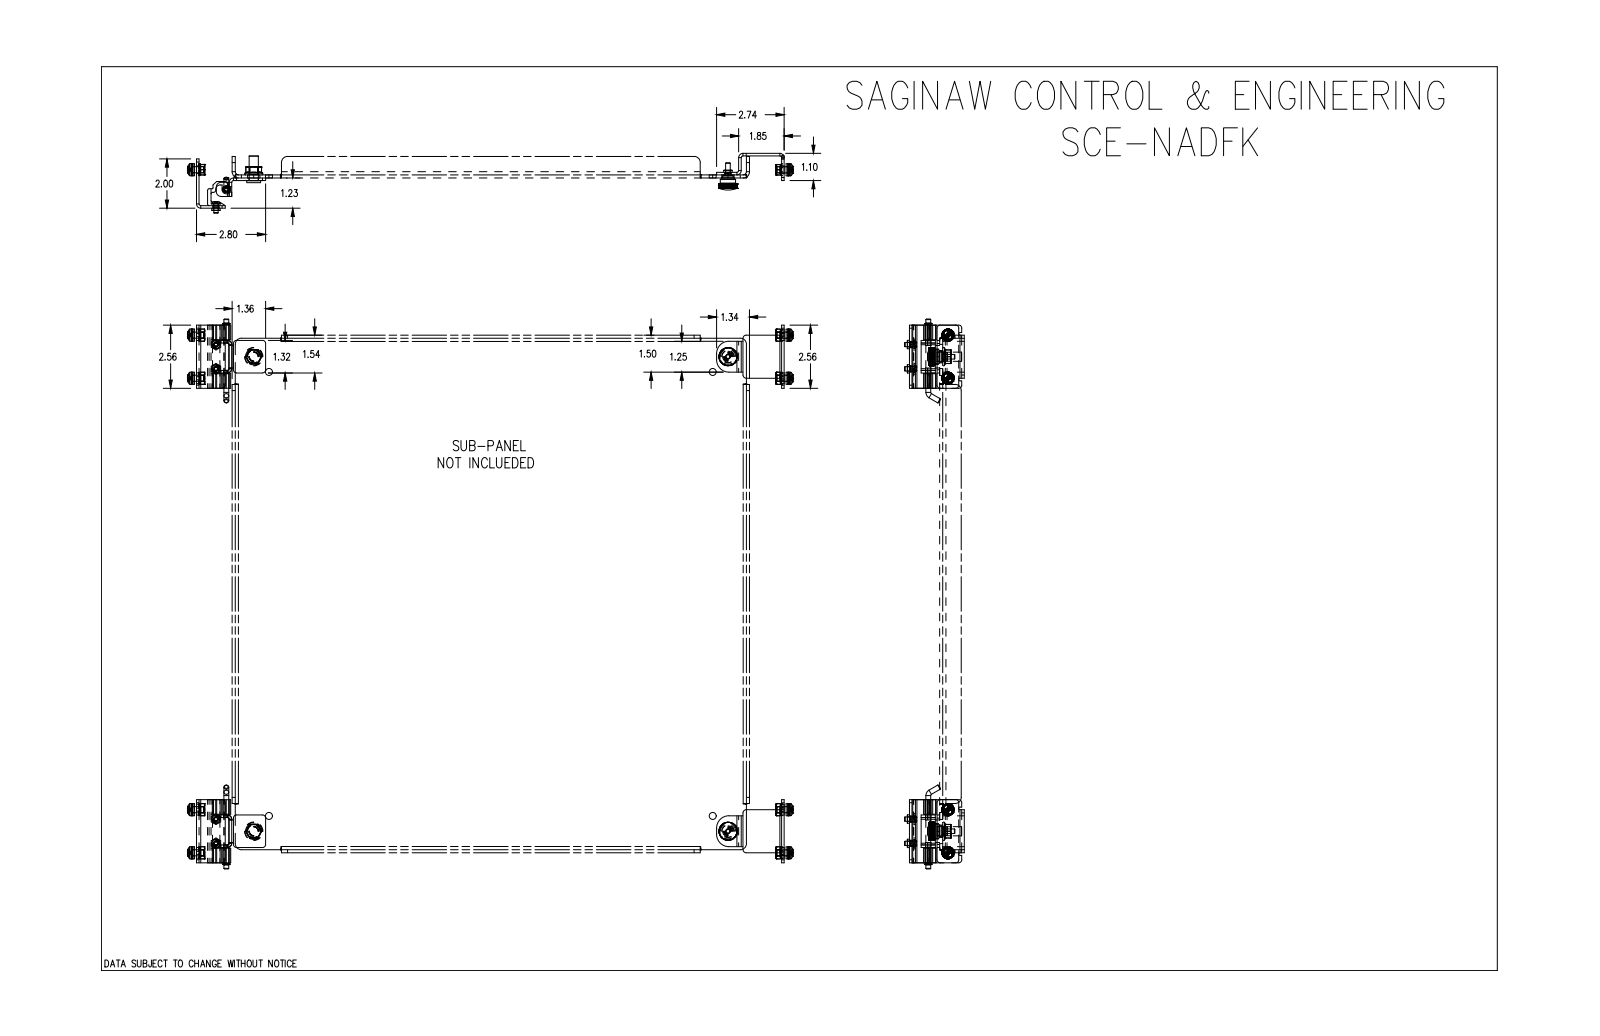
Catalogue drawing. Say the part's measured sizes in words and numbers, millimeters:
The part is named "SCE-NADFK". Its 3-D file was written by "SolidWorks 2019 (CONFIG_CONTROL_DESIGN)". It is 60 solids with 4226 faces: 2230 planar, 1236 cylindrical and 760 other. Overall it measures 624.7 by 566.7 by 61.6 millimeters. Its volume is 108 300 cubic millimeters and its surface area 91 420 square millimeters. Round holes: 14 of diameter 6.4, 8 of diameter 6.3, 6 of diameter 4.8, 4 of diameter 5.1, 2 of diameter 9.3, 2 of diameter 9.5, 1 of diameter 5.3. Round bosses or shafts: 8 of diameter 12.7, 8 of diameter 12.5, 8 of diameter 12.4, 8 of diameter 6.3, 6 of diameter 8.6, 6 of diameter 6.3, 4 of diameter 4.3, 3 of diameter 5. Partial cylindrical surfaces (rounded edges, fillets, slot ends): 546 of radius 0.3, 24 of radius 3.2, 16 of radius 4, 9 of radius 1.8, 9 of radius 4.4, 5 of radius 1.5, 4 of radius 0.1, 4 of radius 1.3. The main face-to-face distances are 2.6, 2.6, 53.9, 25.4, 28.5, 51.3, 56.5, 603.3, 600.6, 605.9. The hole center spacings are 489, 489, 528, 40.9, 44.5, 25, 25, 44.5.
